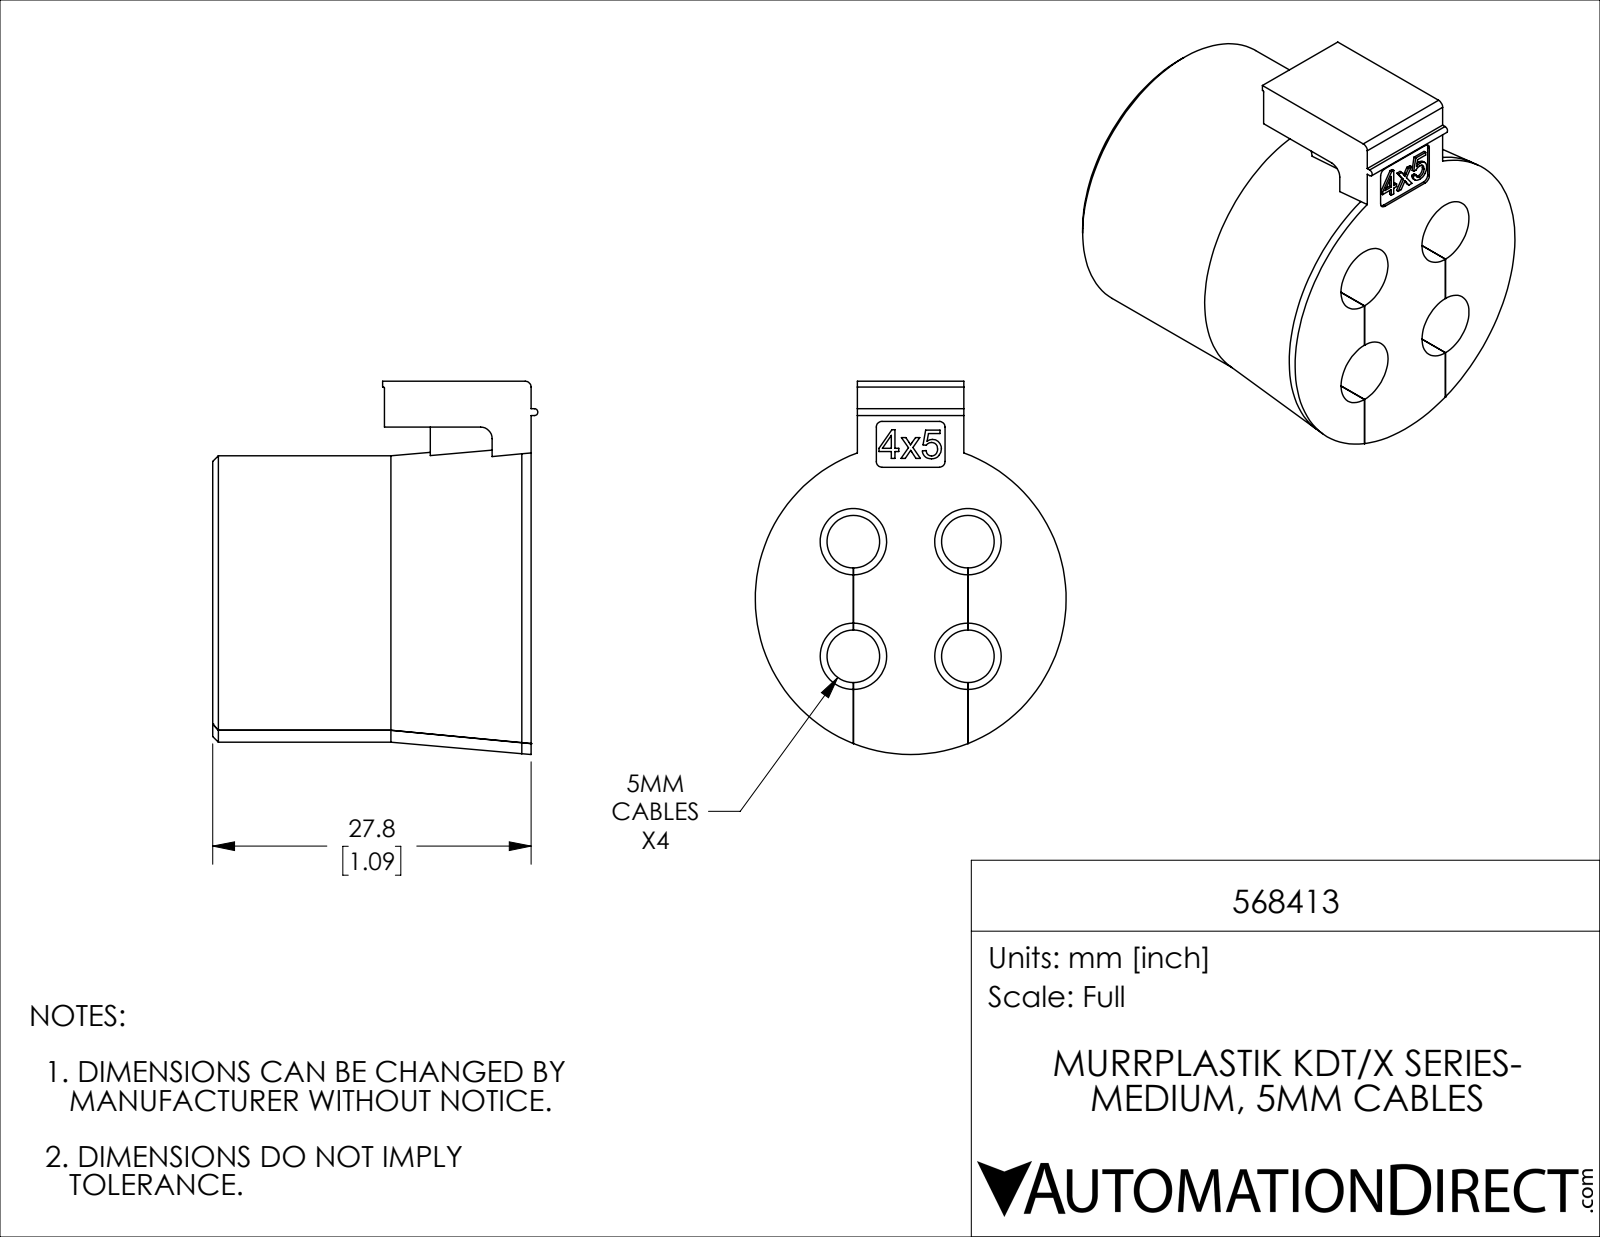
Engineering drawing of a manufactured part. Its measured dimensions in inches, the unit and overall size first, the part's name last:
Units: inches
Overall size (bounding box): 1.282 × 1.118 × 1.069
Round holes (diameter × count): ⌀0.181 ×4, ⌀0.228 ×4
Round bosses / shafts (diameter × count): ⌀0.984 ×1
Partial cylindrical surfaces — rounded edges, fillets, slot ends (radius × count): R0.02 ×5, R0.004 ×1, R0.012 ×1, R0.039 ×1
Main face-to-face distances: 0.393, 1.094, 0.393, 0.394, 0.013, 0.014, 0.38, 0.38, 0.157, 0.366
Hole centre spacings: 0.394, 0.557
Volume: 0.723 in³ · Surface area: 9.923 in²
Bodies: 1 solid, 163 faces (68 planar, 50 cylindrical, 45 other)
Part name (STEP PRODUCT): 568413
STEP written by: SolidWorks 2019 (CONFIG_CONTROL_DESIGN)
